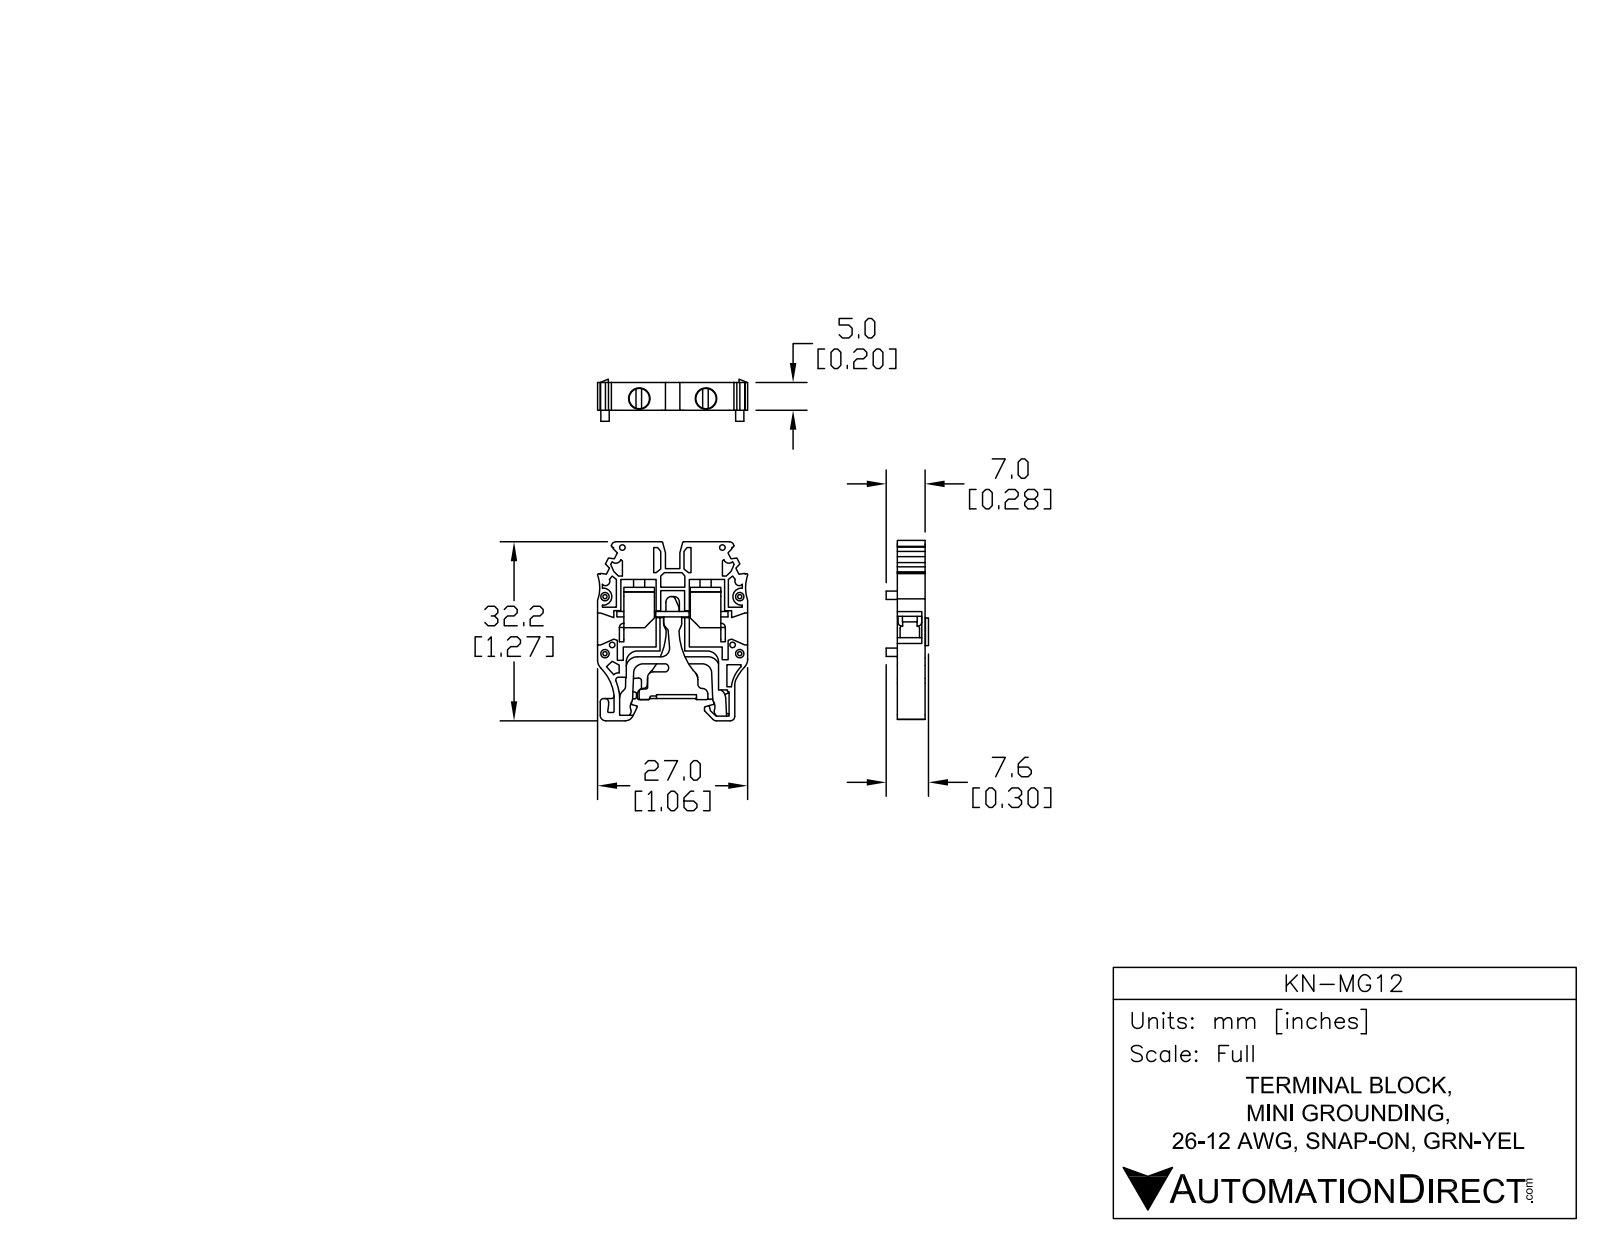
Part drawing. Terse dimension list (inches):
name: KN-MG12
written by: SolidWorks 2014 (AUTOMOTIVE_DESIGN)
unit: in
bodies: 6 solids, 552 faces (361 planar, 191 cylindrical, 0 other)
size: 1.268 × 1.063 × 0.3
volume: 0.127 in³; area: 7.516 in²
holes: 4× ⌀0.039, 4× ⌀0.059, 3× ⌀0.03, 2× ⌀0.079, 2× ⌀0.152, 1× ⌀0.03
bosses: 2× ⌀0.148
rounds: 14× R0.01, 13× R0.008, 13× R0.03, 11× R0.039, 9× R0.02, 8× R0.005, 5× R0.079, 4× R0.016
face distances: 0.024, 0.197, 0.173, 0.039, 0.031, 0.035, 0.138, 0.059, 0.136, 0.079
hole spacings: 0.346, 0.369, 0.404, 0.693, 0.901, 0.966, 1.041, 0.08
